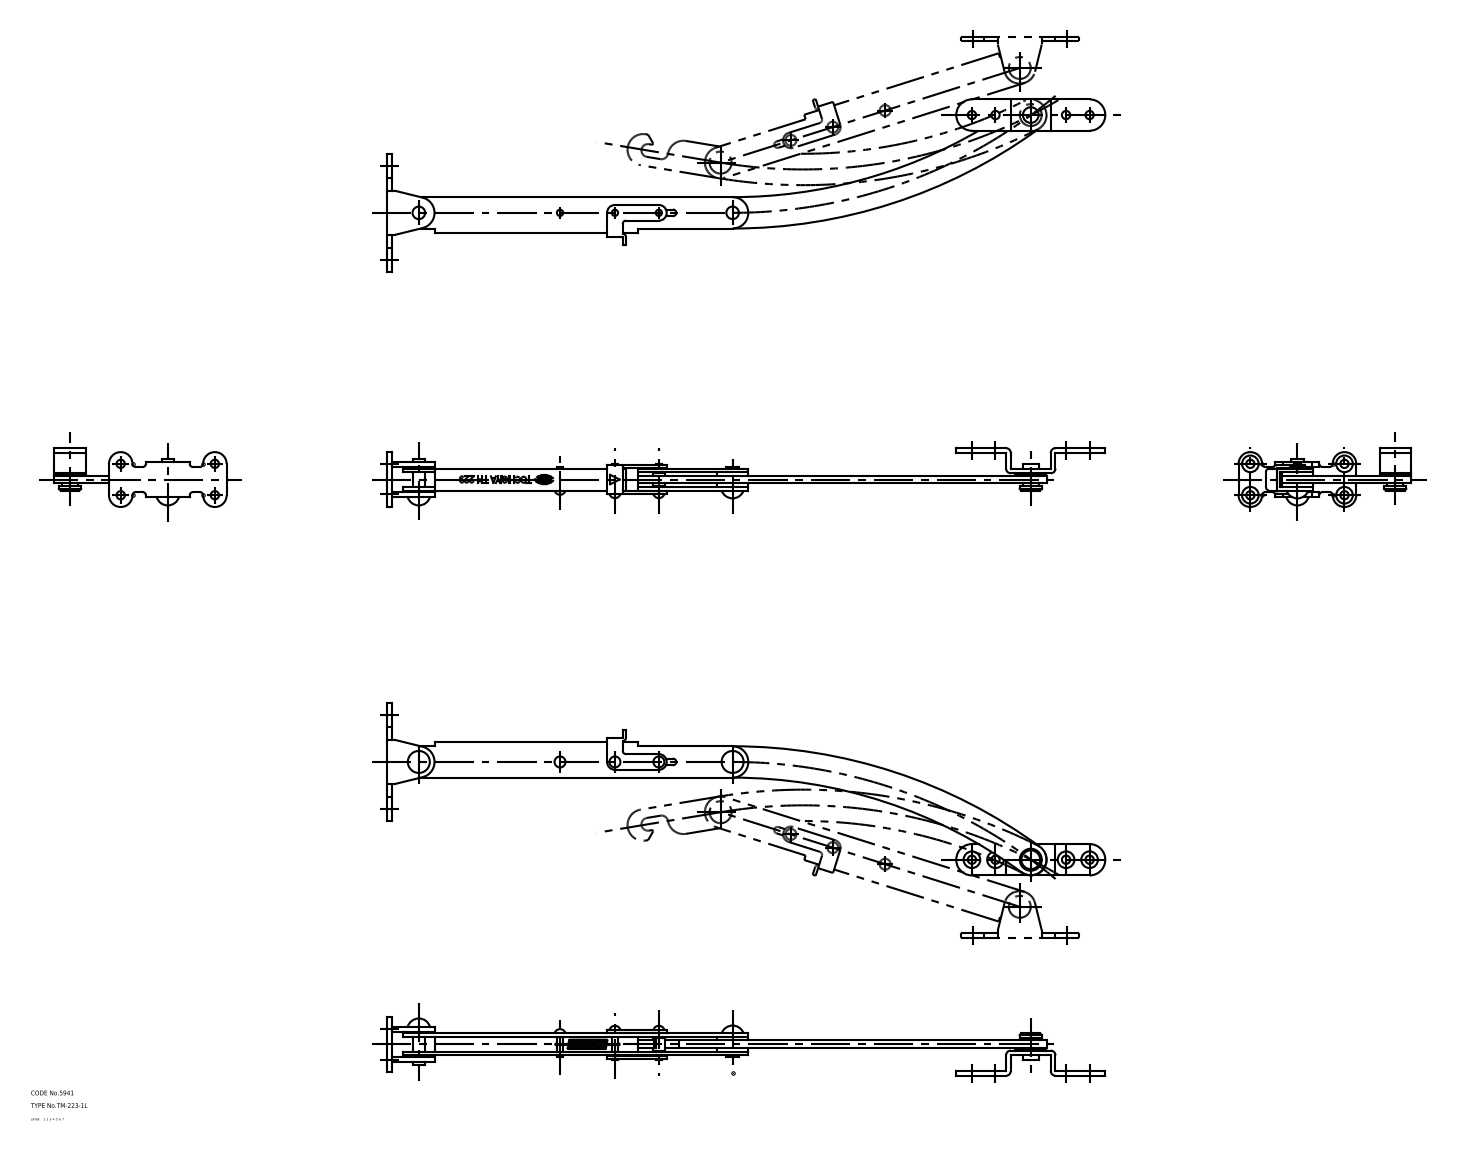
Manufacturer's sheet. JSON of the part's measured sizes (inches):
{"part_name": "spacer_A; spacer_C; pin_A; stopper (+8 more)", "step_written_by": "CADfix (AUTOMOTIVE_DESIGN)", "units": "inches", "bodies": {"solids": 18, "faces": 301, "planar": 0, "cylindrical": 0, "other": 301}, "overall_size": [18.013, 4.324, 1.476], "volume_in3": 4.251, "surface_area_in2": 91.23}
